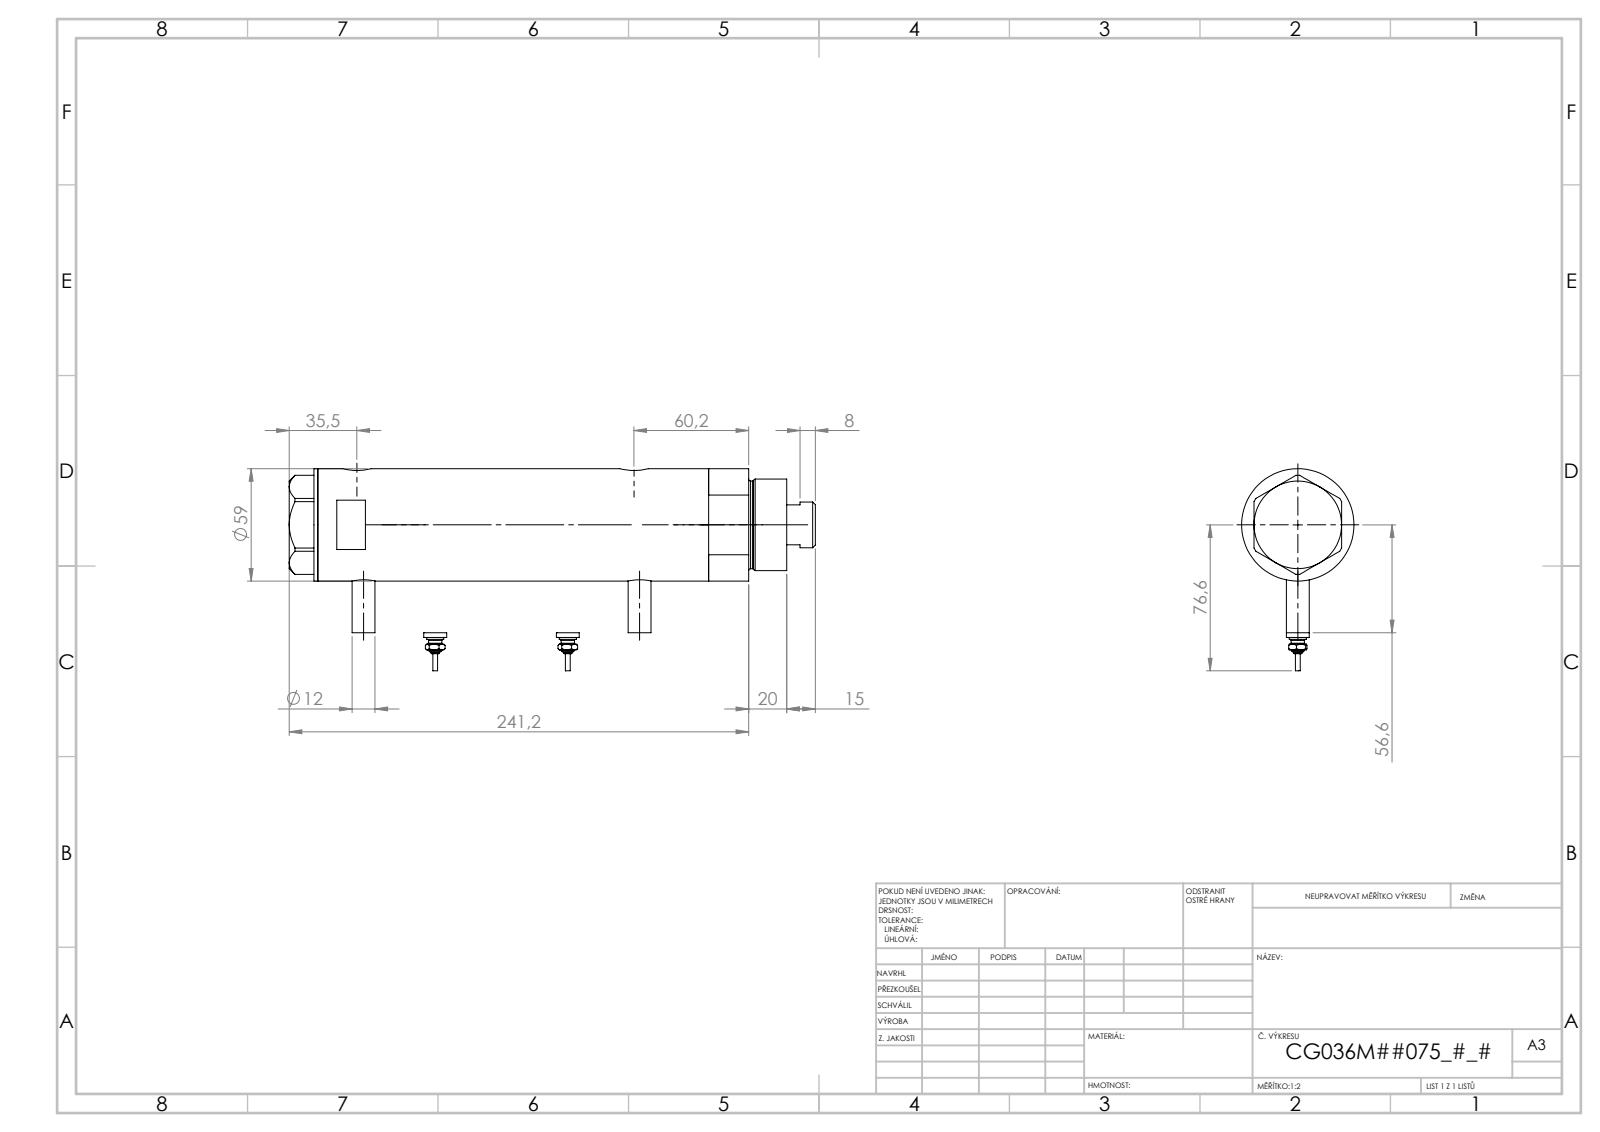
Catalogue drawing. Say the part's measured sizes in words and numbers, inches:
The part is named "V270CG_FRONT; V270CG_VC; V270CG_BACK; V270CG_MIDDLE (+1 more)". Its 3-D file was written by "SolidWorks 2019 (CONFIG_CONTROL_DESIGN)". It is 6 solids with 232 faces: 81 planar, 77 cylindrical and 74 other. Overall it measures 9.387 by 3.594 by 2.323 inches. Its volume is 32.92 cubic inches and its surface area 173.8 square inches. Round holes: 2 of diameter 0.197, 2 of diameter 0.383, 2 of diameter 0.492, 2 of diameter 0.591, 1 of diameter 0.335, 1 of diameter 0.984, 1 of diameter 1.043, 1 of diameter 1.417, 1 of diameter 1.575, 1 of diameter 2.047. Round bosses or shafts: 4 of diameter 0.472, 2 of diameter 0.354, 2 of diameter 0.276, 2 of diameter 0.171, 2 of diameter 0.094, 1 of diameter 2.323, 1 of diameter 1.89, 1 of diameter 1.811. The main face-to-face distances are 0.925, 0.591, 1.516, 5.801, 5.21, 4.285, 8.796, 8.206, 7.28, 2.995. The hole center spacings are 0.114, 0.138, 4.219, 4.333, 4.356, 4.47, 0.114, 0.115.
